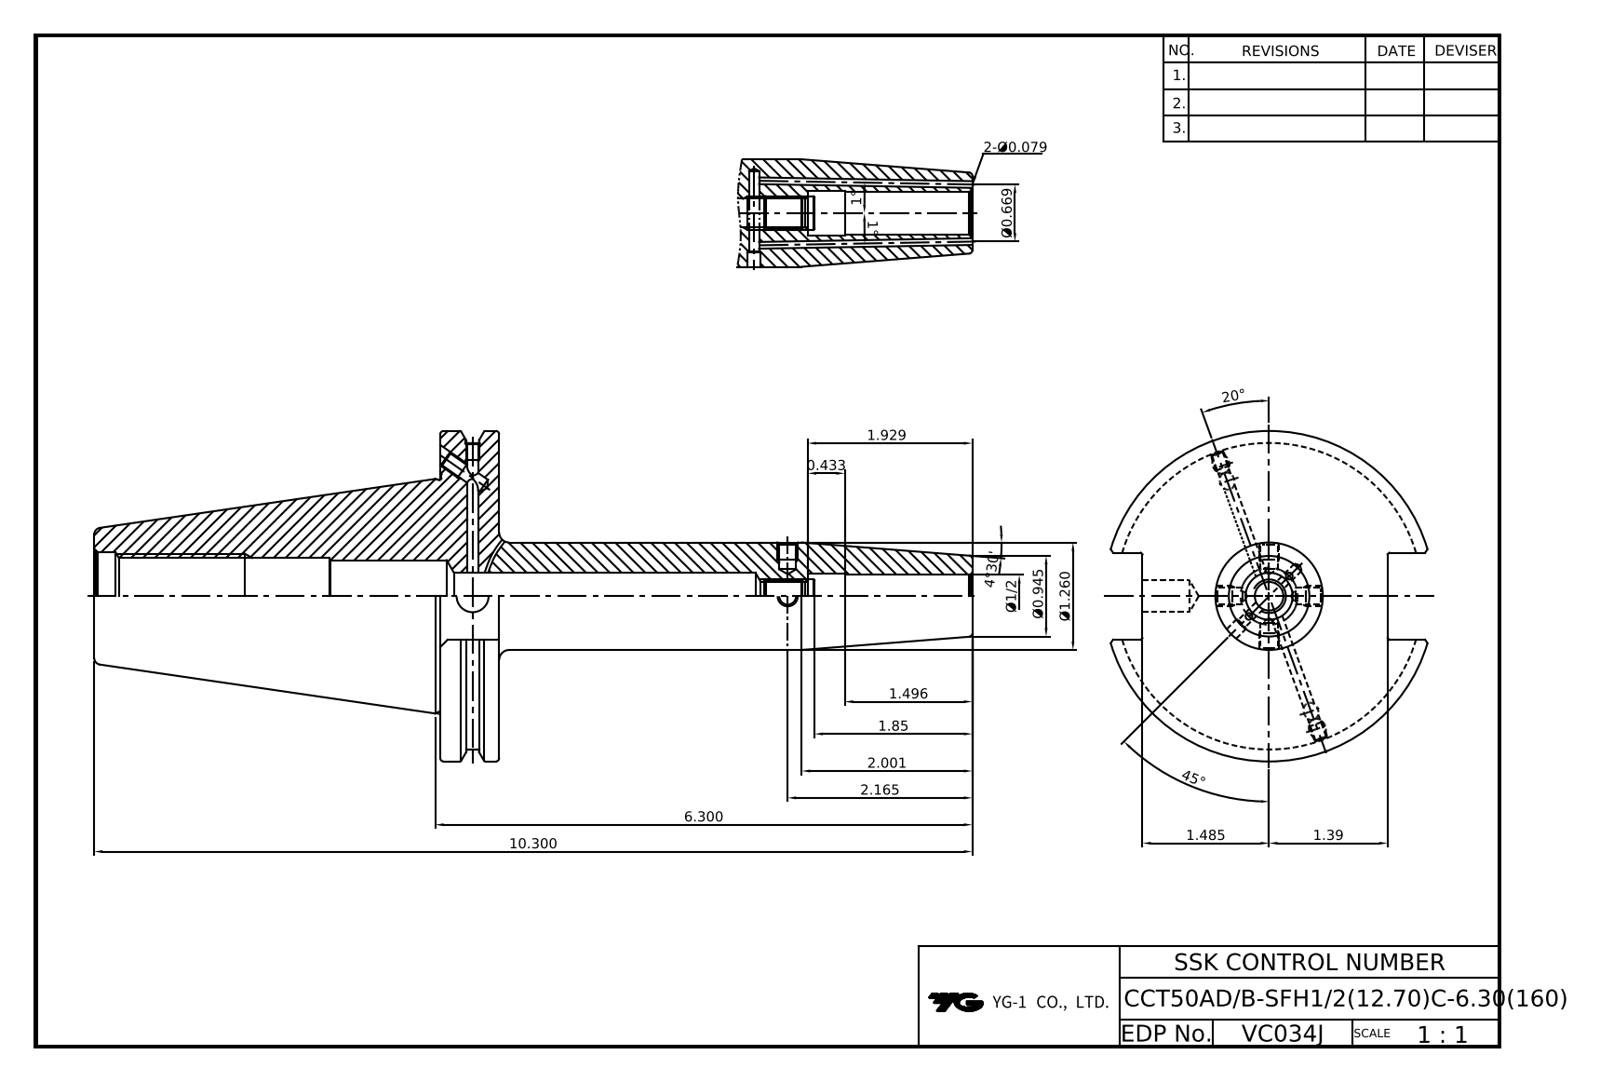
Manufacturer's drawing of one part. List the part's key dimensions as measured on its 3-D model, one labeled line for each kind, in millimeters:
Part name (STEP PRODUCT): LO-CCT50ADB-SFH12.7C-6.30
STEP written by: Autodesk Inventor 2025 (AUTOMOTIVE_DESIGN)
Units: millimetres
Bodies: 1 solid, 92 faces (38 planar, 29 cylindrical, 25 other)
Overall size (bounding box): 261.6 × 98.42 × 94.69
Volume: 410 888 mm³ · Surface area: 64 789 mm²
Round holes (diameter × count): ⌀2.5 ×2, ⌀3.24 ×2, ⌀4.13 ×2, ⌀4.2 ×2, ⌀5 ×2, ⌀8.92 ×1, ⌀9.53 ×1, ⌀12.7 ×1, ⌀13.9 ×1, ⌀14 ×1, ⌀21.97 ×1, ⌀26.2 ×1
Round bosses / shafts (diameter × count): ⌀98.42 ×1, ⌀91.29 ×1, ⌀69.25 ×1, ⌀32 ×1
Main face-to-face distances: 17.55, 103.1, 120.65, 73.03, 25.9, 103.5, 0.4, 17.15, 261.6, 158.5
